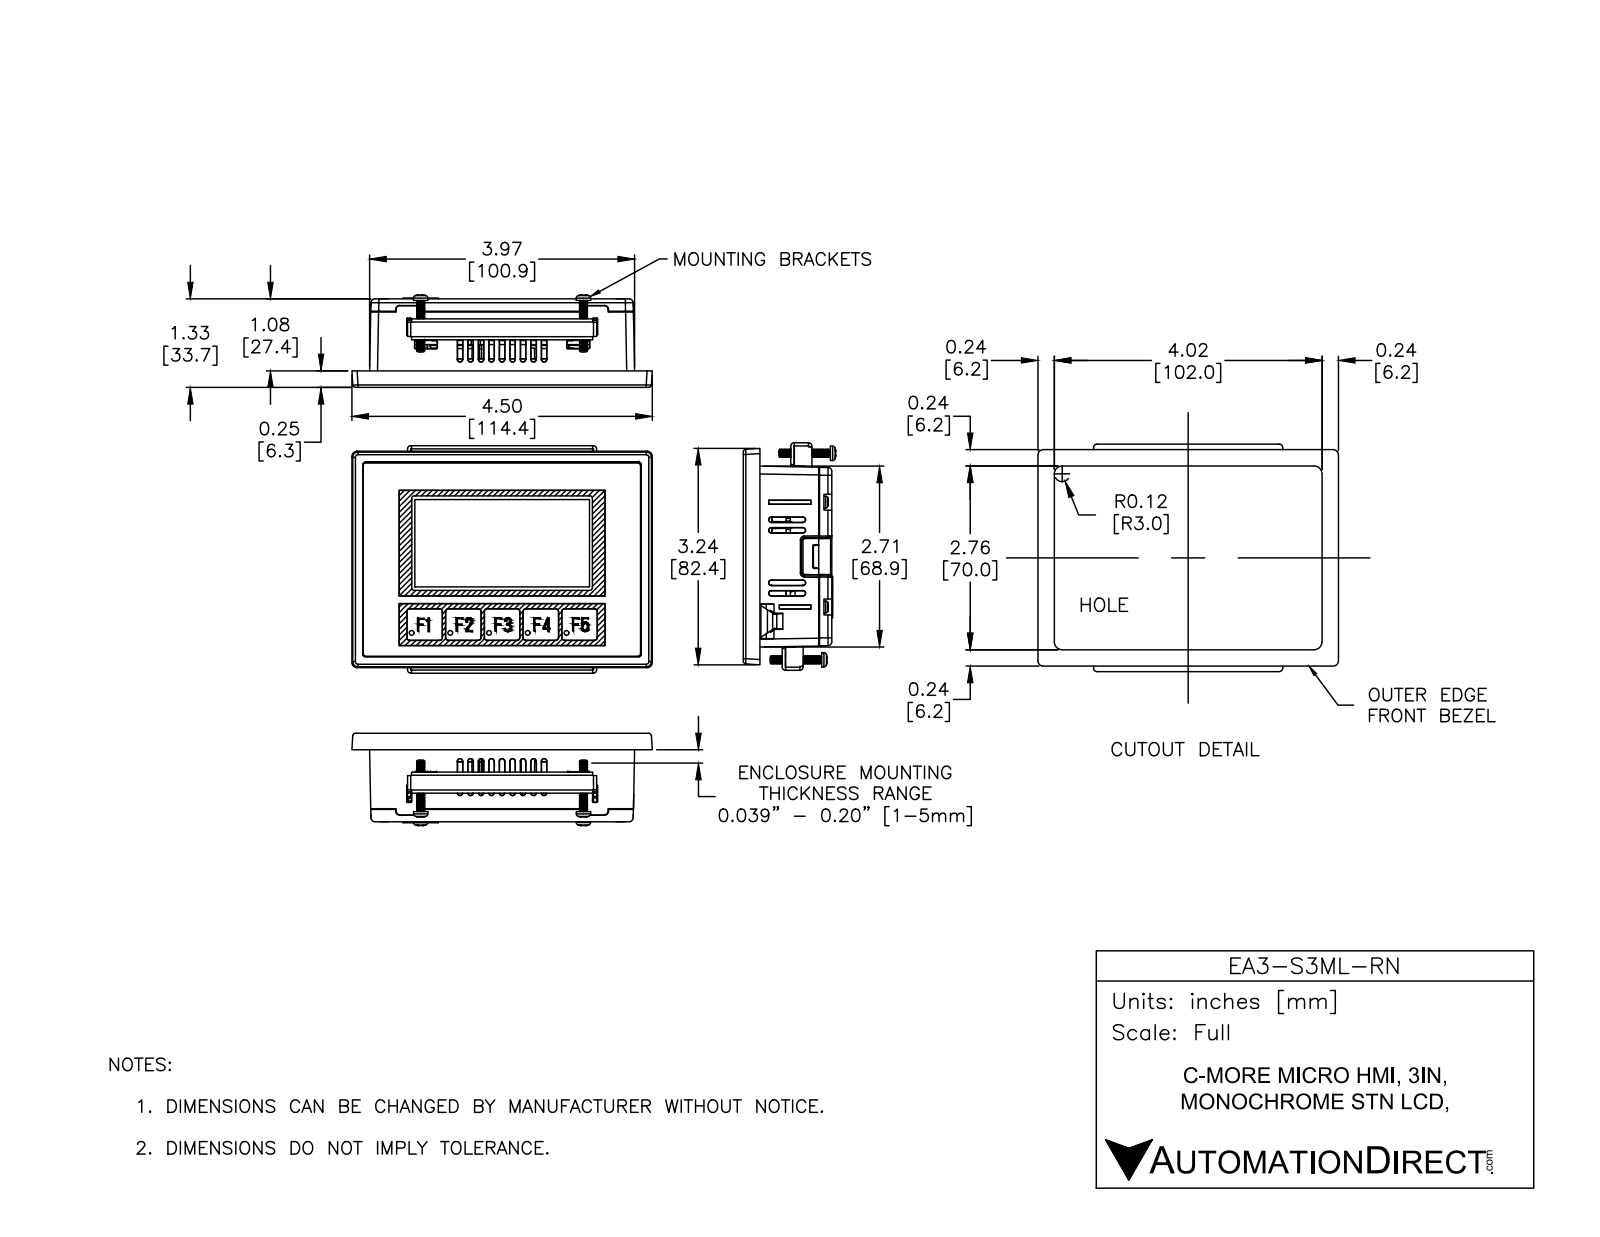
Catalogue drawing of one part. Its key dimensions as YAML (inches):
part_name: "EA3-S3ML-RN"
step_written_by: "SolidWorks 2017 (AUTOMOTIVE_DESIGN)"
units: inches
bodies: {solids: 1, faces: 1759, planar: 1028, cylindrical: 321, other: 410}
overall_size: [4.504, 3.409, 1.386]
volume: 14.72
surface_area: 73.23
round_holes:
  - {diameter: 0.071, count: 5}
  - {diameter: 0.122, count: 4}
round_bosses_or_shafts:
  - {diameter: 0.217, count: 4}
  - {diameter: 0.177, count: 4}
  - {diameter: 0.118, count: 4}
  - {diameter: 0.087, count: 4}
partial_cylinders:
  - {radius: 0.02, count: 37}
  - {radius: 0.039, count: 30}
  - {radius: 0.016, count: 16}
  - {radius: 0.059, count: 12}
  - {radius: 0.118, count: 10}
  - {radius: 0.012, count: 8}
  - {radius: 0.047, count: 8}
  - {radius: 0.066, count: 4}
face_to_face_distances: [1.318, 1.313, 0.047, 0.268, 0.315, 1.205, 0.113, 0.108, 0.248, 0.111]
hole_center_spacings: [0.581, 1.161, 1.742, 2.441, 3.095, 3.942, 0.465, 0.512]
